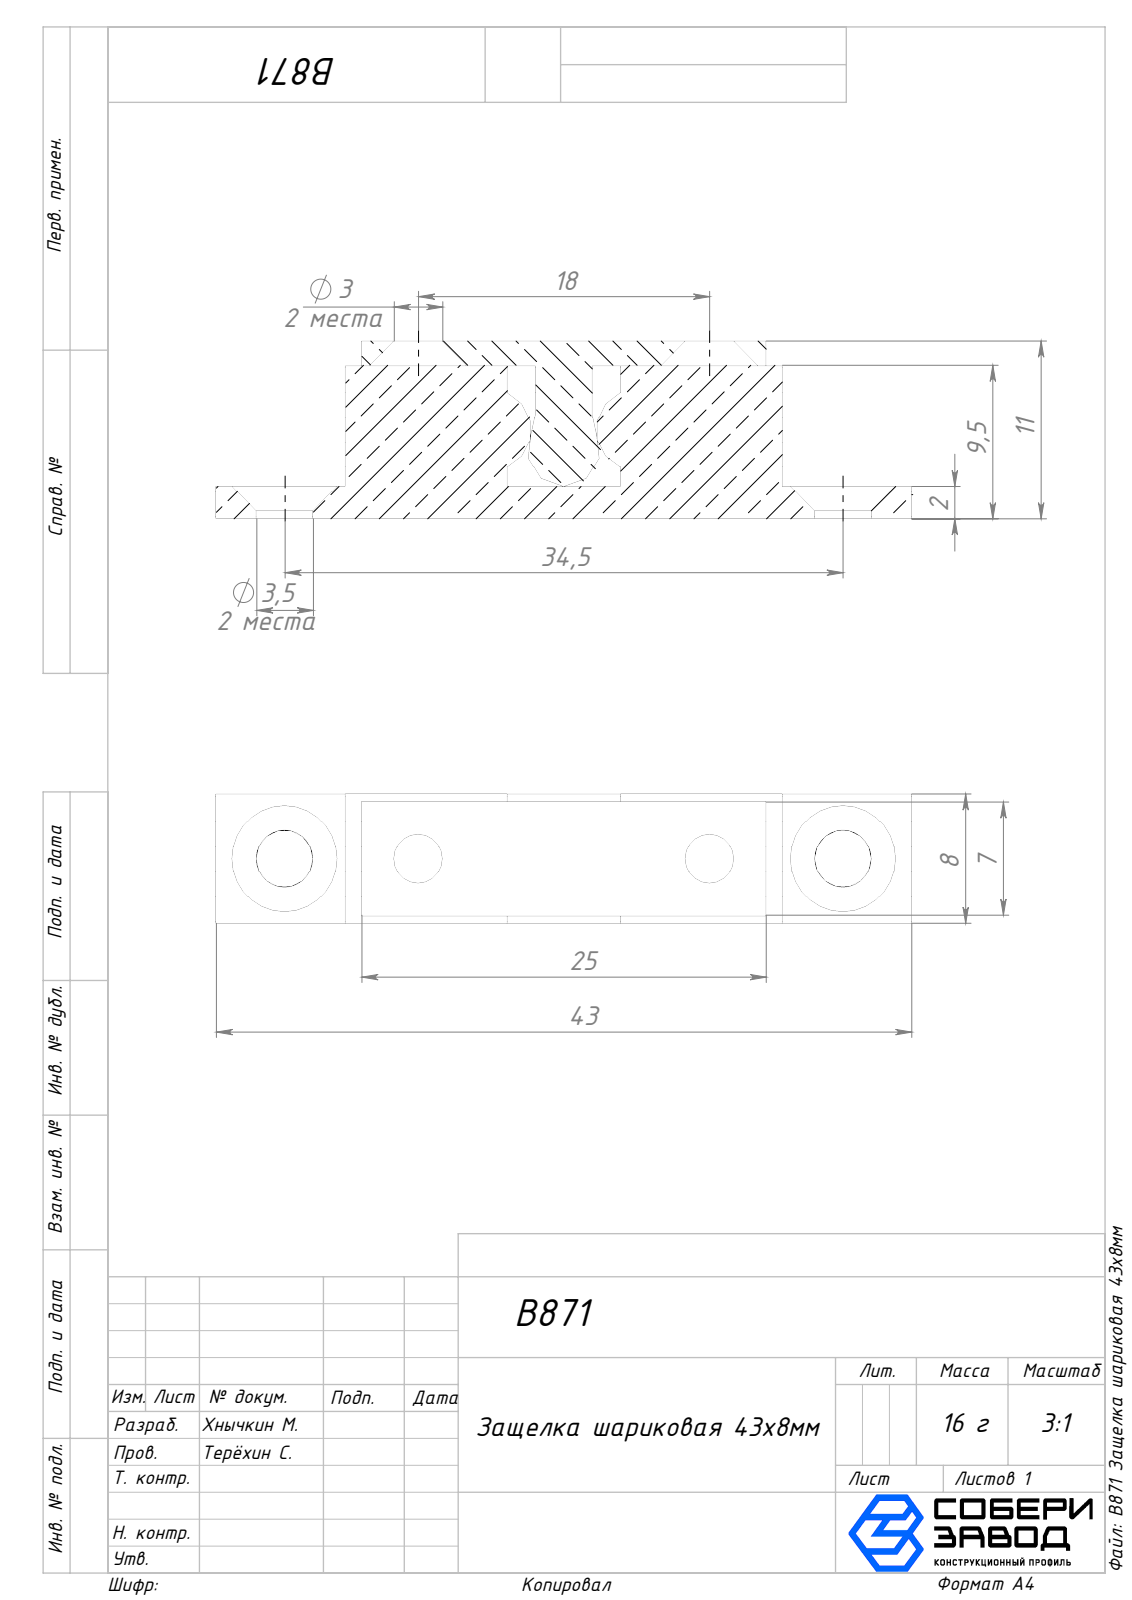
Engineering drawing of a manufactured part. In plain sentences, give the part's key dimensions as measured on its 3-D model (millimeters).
The part is named "Часть_1_00; B871 Защелка шариковая 43х8мм; 2 часть_00". Its 3-D file was written by "SolidWorks 2025 (AUTOMOTIVE_DESIGN)". It is 2 solids with 42 faces: 21 planar, 11 cylindrical and 10 other. Overall it measures 43 by 11 by 8 millimeters. Its volume is 2 113 cubic millimeters and its surface area 1 932 square millimeters. Round holes: 2 of diameter 3.5. Partial cylindrical surfaces (rounded edges, fillets, slot ends): 2 of radius 3, 1 of radius 2.25, 1 of radius 4. The main face-to-face distances are 7.5, 8, 11, 9, 0.5, 2, 7, 9.5, 1.5, 10. The hole center spacings are 34.5.
